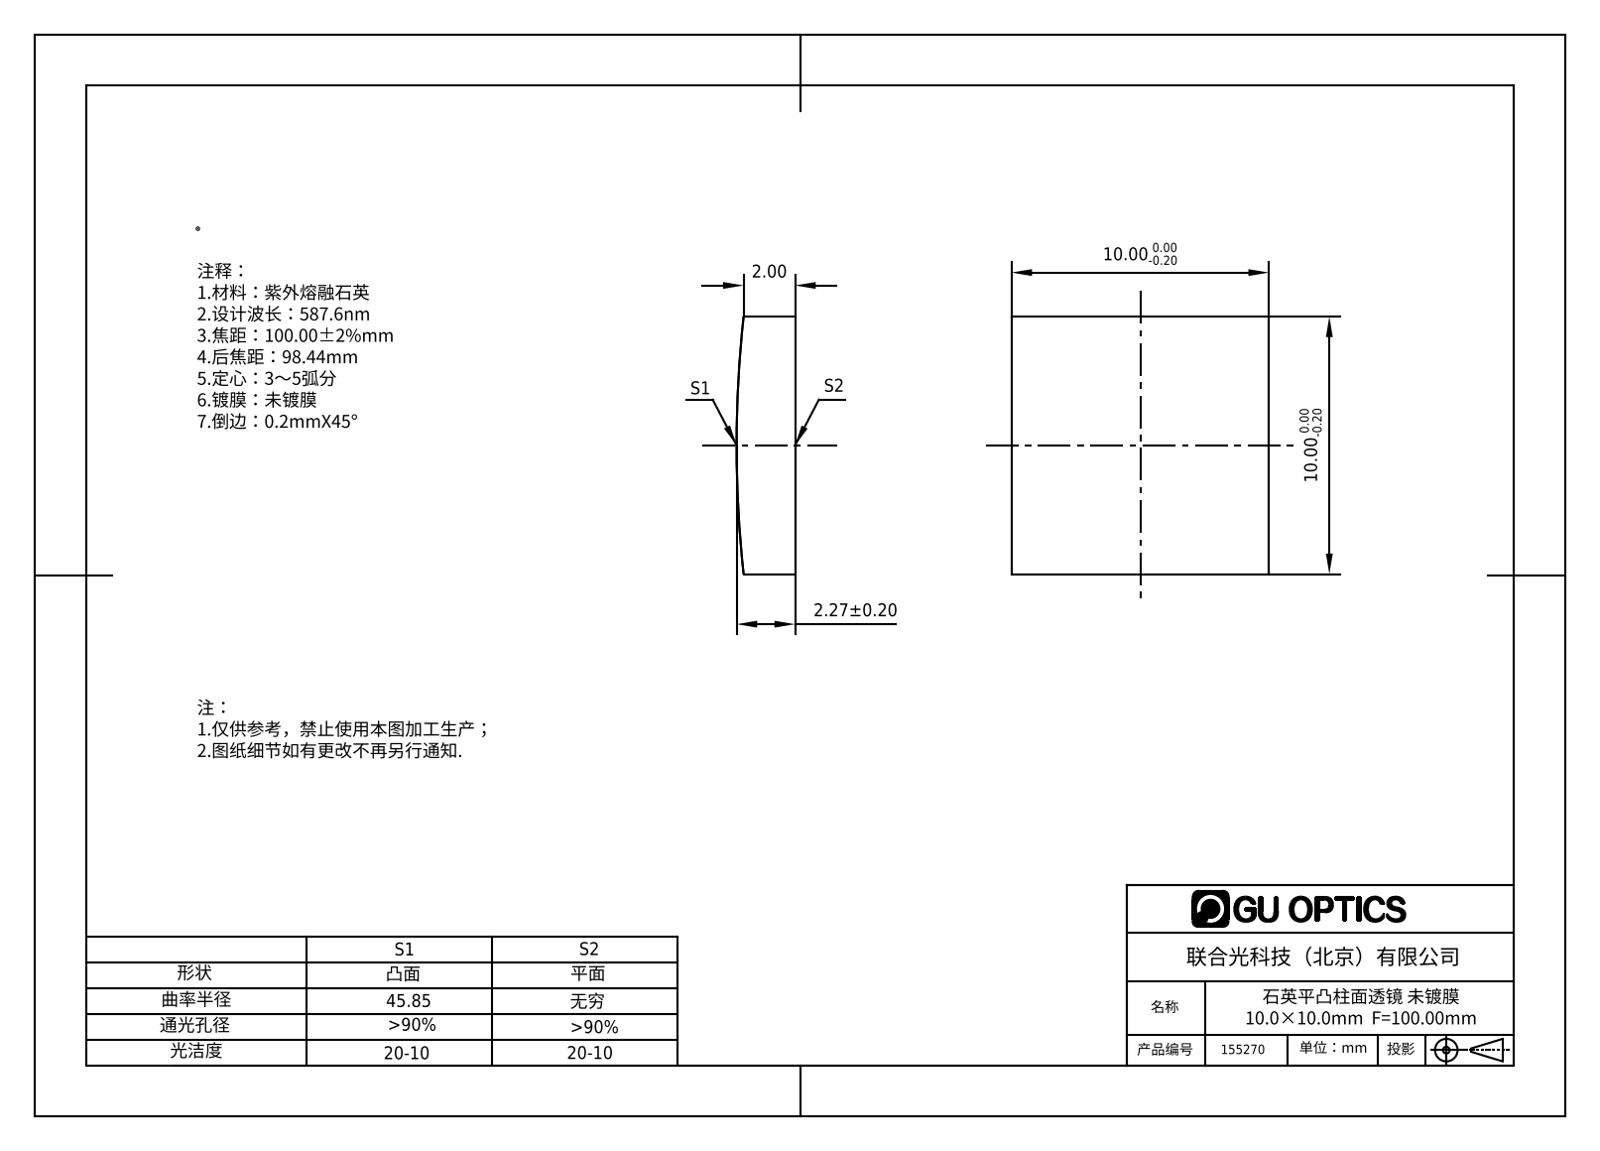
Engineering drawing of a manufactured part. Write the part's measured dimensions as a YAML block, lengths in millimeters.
part_name: "155270"
step_written_by: "SolidWorks 2016 (AUTOMOTIVE_DESIGN)"
units: millimeters
bodies: {solids: 1, faces: 6, planar: 5, cylindrical: 1, other: 0}
overall_size: [10, 10, 2.27]
volume: 218
surface_area: 284
partial_cylinders:
  - {radius: 45.85, count: 1}
face_to_face_distances: [10]
